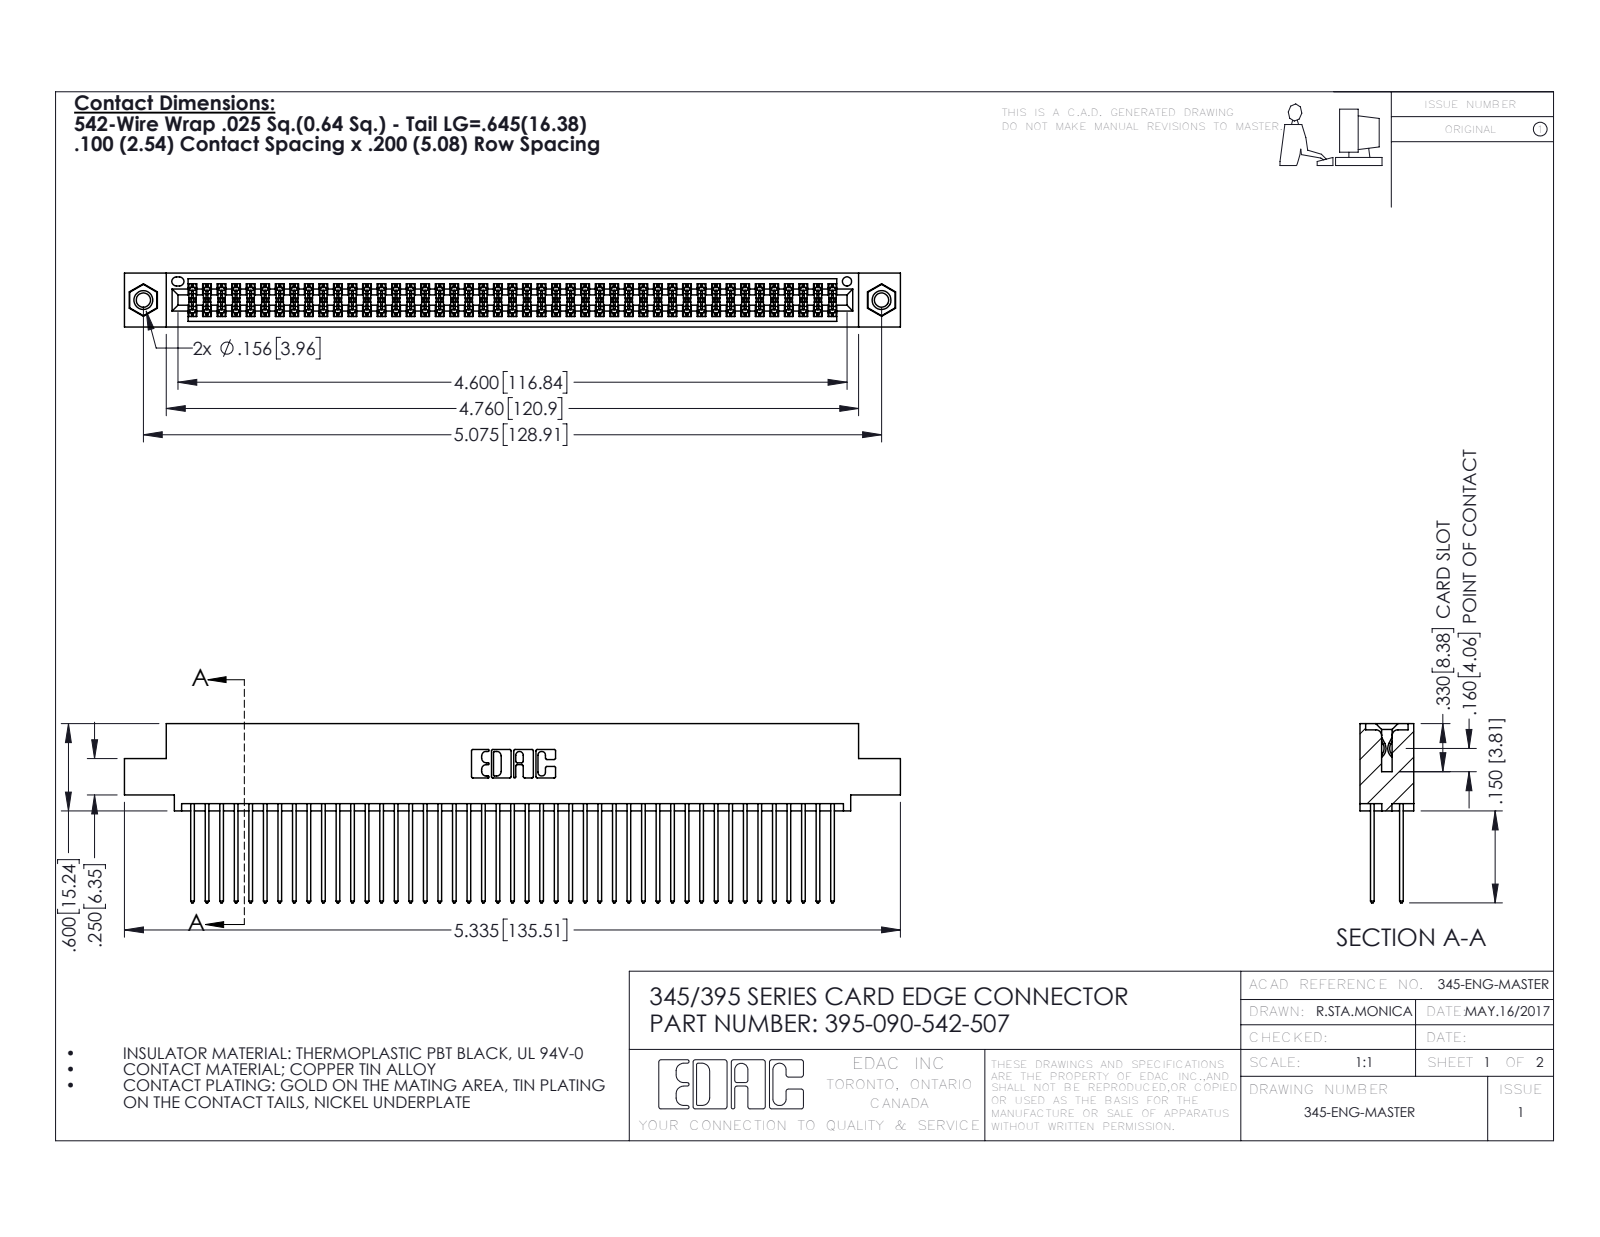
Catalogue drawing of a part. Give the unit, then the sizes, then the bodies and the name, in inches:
Units: inches
Overall size (bounding box): 5.335 × 1.232 × 0.37
Round holes (diameter × count): ⌀0.098 ×2, ⌀0.125 ×2, ⌀0.156 ×2, ⌀0.064 ×1
Round bosses / shafts (diameter × count): ⌀0.155 ×2
Partial cylindrical surfaces — rounded edges, fillets, slot ends (radius × count): R0.006 ×135, R0.01 ×90, R0.01 ×22, R0.007 ×6, R0.031 ×6, R0.026 ×3, R0.014 ×2, R0.019 ×2
Main face-to-face distances: 0.072, 0.298, 0.2, 0.098, 0.272, 0.025, 0.225, 0.37, 0.175, 0.149
Hole centre spacings: 0.27, 4.839, 5.075
Volume: 0.825 in³ · Surface area: 34.3 in²
Bodies: 93 solids, 4690 faces (3086 planar, 1588 cylindrical, 16 other)
Part name (STEP PRODUCT): 395-090-542-507; 345-292-001_345-293-142; 345-250-001_345-250-005-103; 345 Part_0.110 Offset - 0.156 Dia-TI
STEP written by: SolidWorks 2016 (CONFIG_CONTROL_DESIGN)
